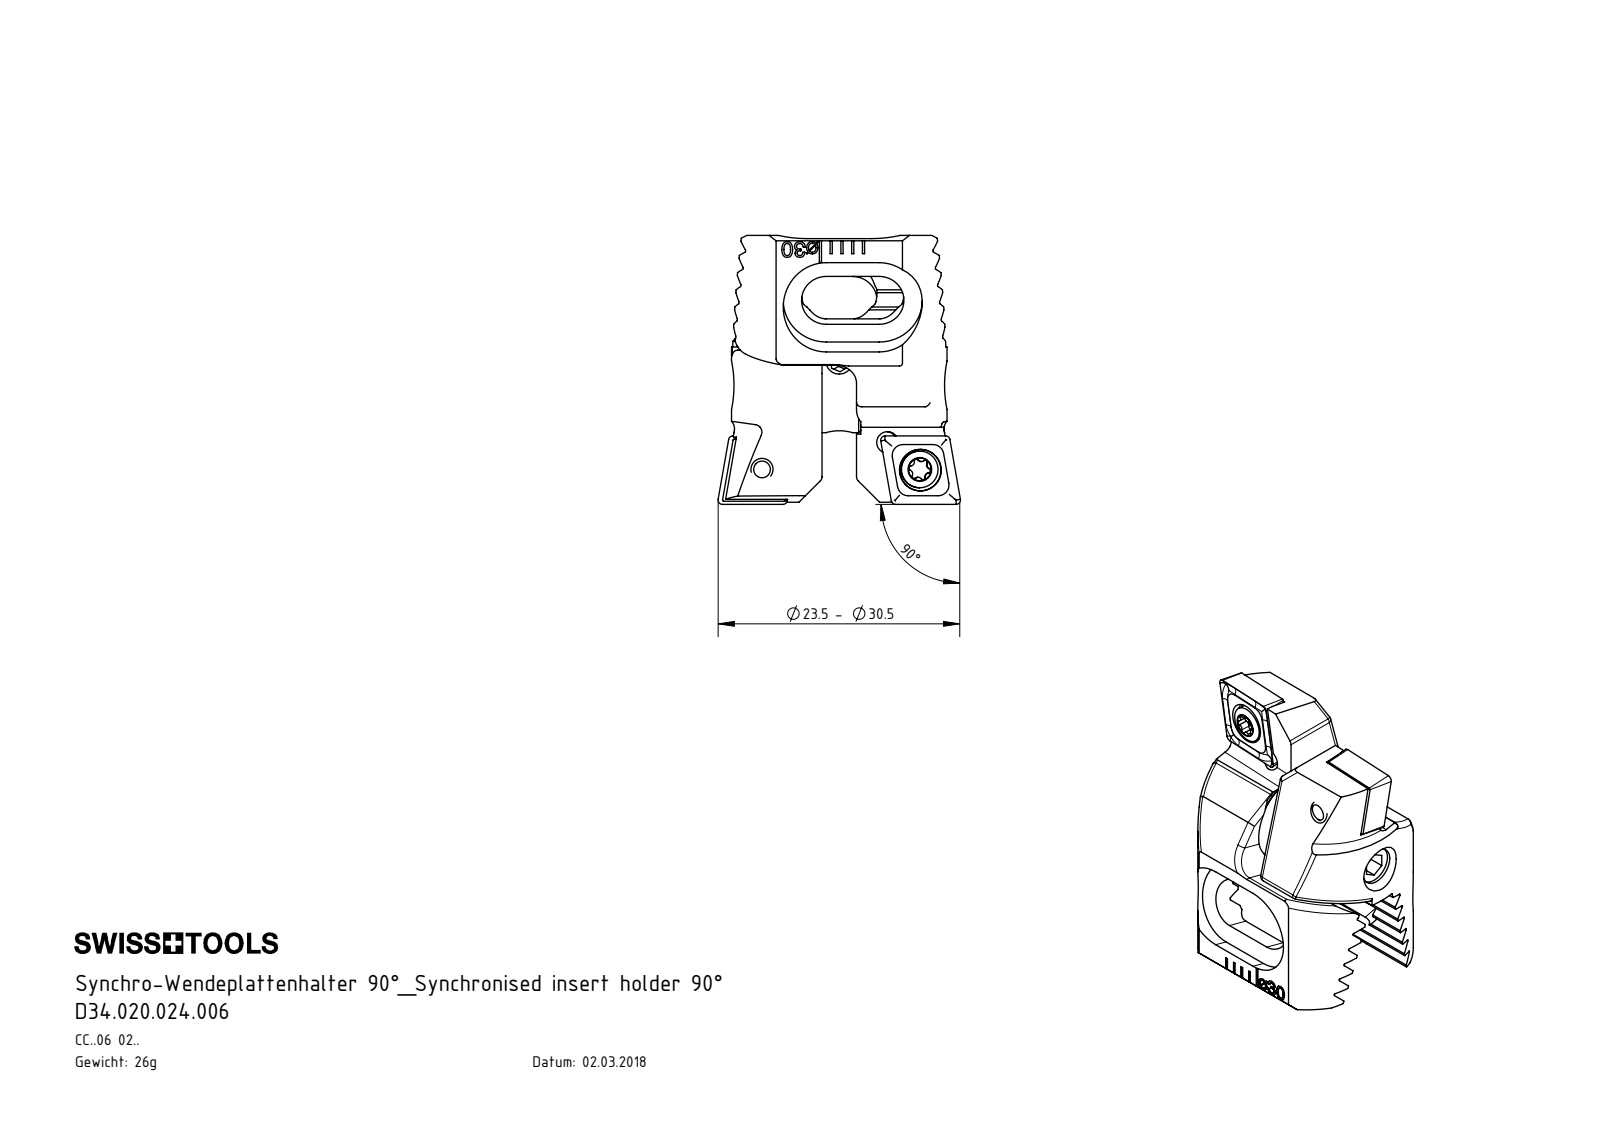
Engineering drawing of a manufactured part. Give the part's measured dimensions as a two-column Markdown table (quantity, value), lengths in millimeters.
| quantity | value |
| --- | --- |
| part name | D34.020.024.006; ISO 4026 - M3 x 2; WCA-ER2.001.006_A; CCMT060204 (+4 more) |
| STEP written by | SolidWorks 2017 (CONFIG_CONTROL_DESIGN) |
| units | millimeters |
| bodies | 11 solids, 485 faces (189 planar, 158 cylindrical, 138 other) |
| overall size | 24.95 × 22.42 × 16.3 |
| volume | 3 171 mm³ |
| surface area | 3 798 mm² |
| round holes (diameter × count) | 1 × 3, 2.5 × 3, 2 × 2, 2.05 × 2, 2.8 × 2, 3.85 × 2, 3.5 × 1, 9.1 × 1 |
| round bosses / shafts (diameter × count) | 3 × 4, 3.4 × 2, 2.5 × 2, 8.8 × 1, 4 × 1 |
| partial cylindrical surfaces (radius × count) | 0.12 × 12, 0.21 × 12, 0.36 × 10, 1 × 8, 0.5 × 4, 2.3 × 4, 4 × 4, 0.36 × 2 |
| main face-to-face distances | 1.43, 2.86, 4.29, 4, 5.72, 2.57, 3.85, 7.14, 5.71, 0.42 |
| hole center spacings | 3.99, 4.09, 12.02, 12.12, 14.88, 2, 5.99, 6 |
